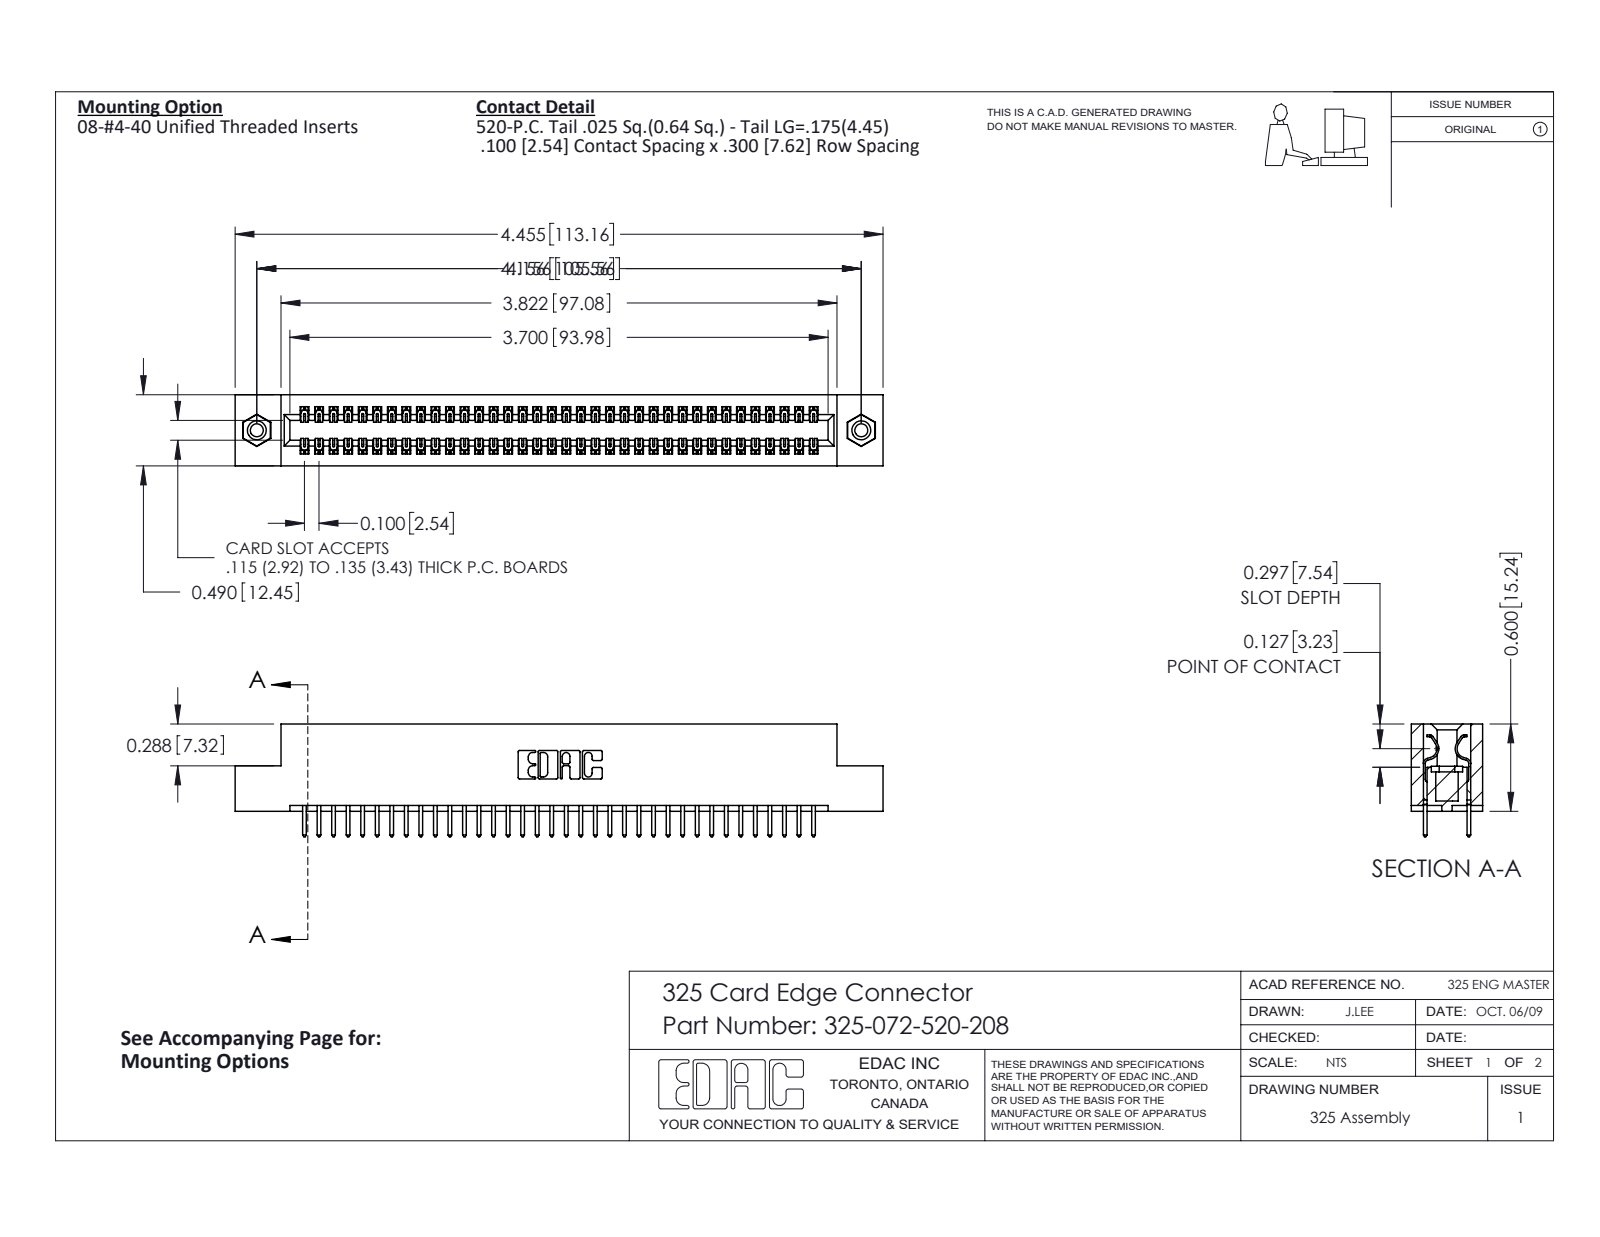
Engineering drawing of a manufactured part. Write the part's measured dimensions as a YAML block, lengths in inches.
part_name: "325-292-001_325-293-120; 325-072-520-208; 325 Part_TI; 345-250-001_345-250-003-102"
step_written_by: "SolidWorks 2016 (CONFIG_CONTROL_DESIGN)"
units: inches
bodies: {solids: 75, faces: 3918, planar: 2694, cylindrical: 1208, other: 16}
overall_size: [4.455, 0.775, 0.49]
volume: 0.887
surface_area: 26.85
round_holes:
  - {diameter: 0.089, count: 2}
  - {diameter: 0.125, count: 2}
  - {diameter: 0.16, count: 2}
round_bosses_or_shafts:
  - {diameter: 0.155, count: 2}
partial_cylinders:
  - {radius: 0.006, count: 108}
  - {radius: 0.01, count: 72}
  - {radius: 0.01, count: 22}
  - {radius: 0.007, count: 6}
  - {radius: 0.031, count: 6}
  - {radius: 0.026, count: 3}
  - {radius: 0.014, count: 2}
  - {radius: 0.022, count: 2}
face_to_face_distances: [0.083, 0.407, 0.49, 0.3, 0.107, 0.383, 0.025, 0.325, 0.275, 0.56]
hole_center_spacings: [4.156]
